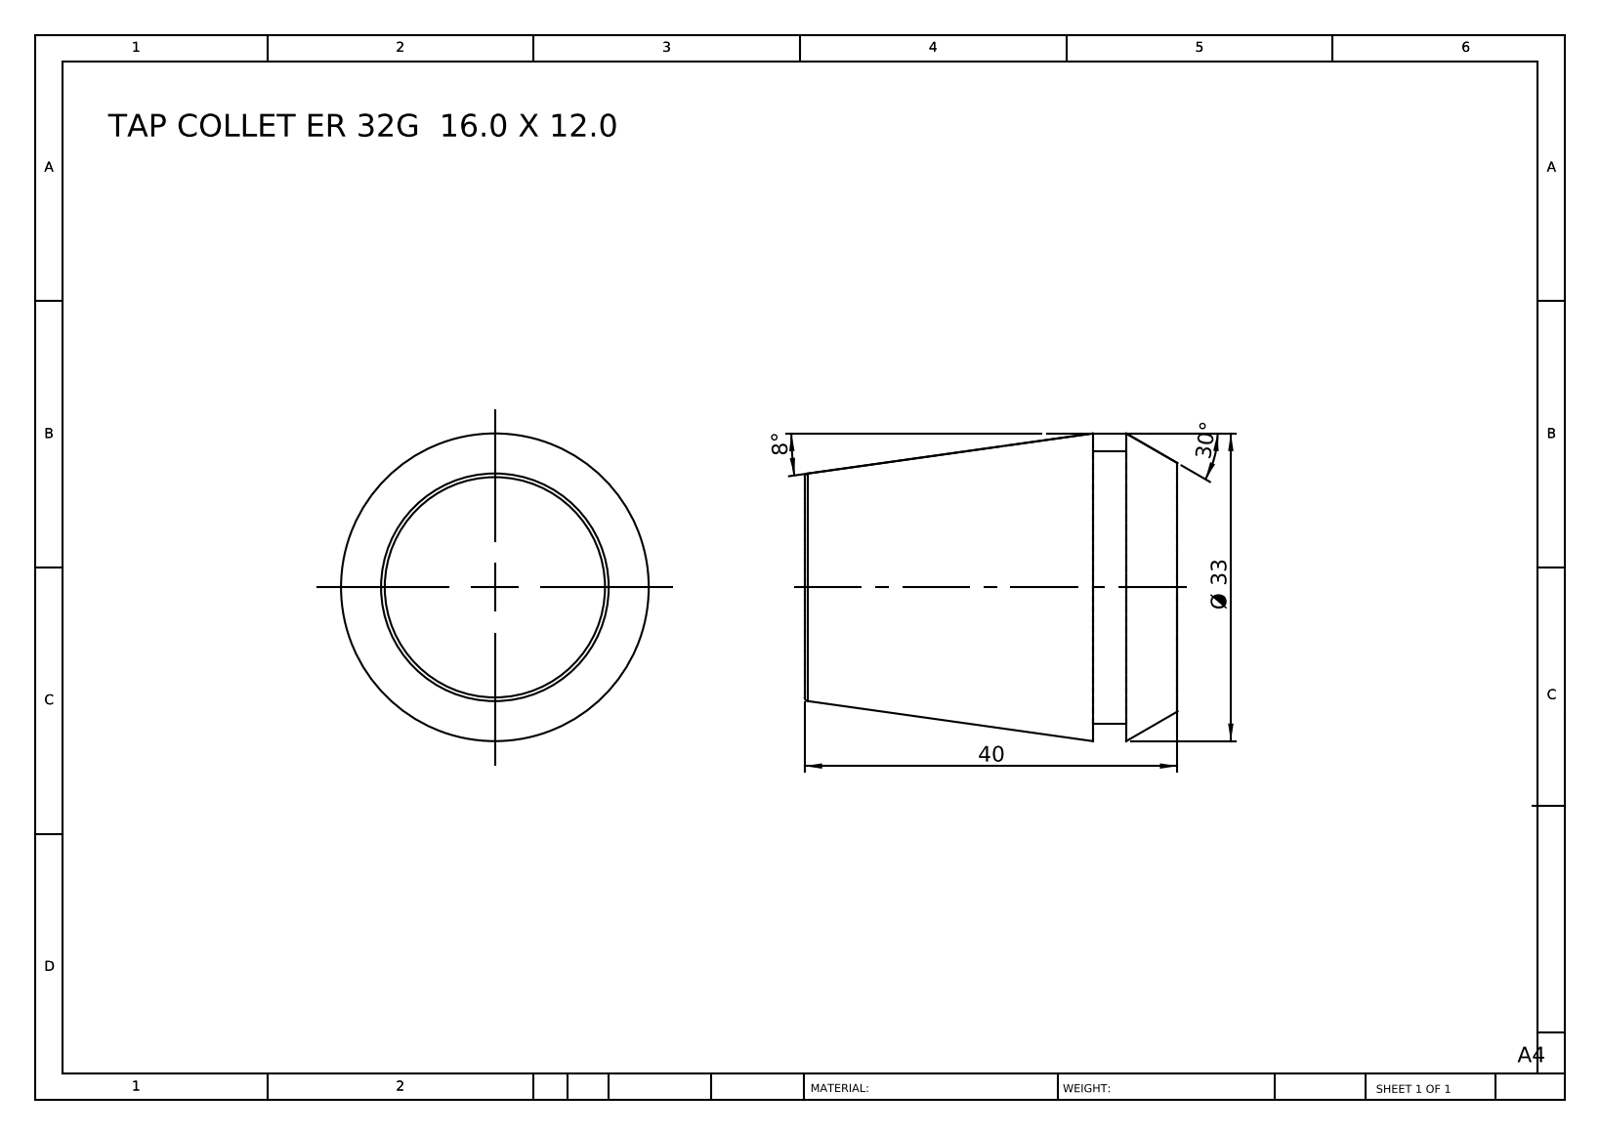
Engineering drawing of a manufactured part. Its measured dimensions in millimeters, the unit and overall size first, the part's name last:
Units: millimetres
Overall size (bounding box): 40 × 33 × 33
Round bosses / shafts (diameter × count): ⌀29.2 ×1
Main face-to-face distances: 40, 9.1, 30.9, 5.5, 3.6, 34.5
Volume: 26 350 mm³ · Surface area: 5 119 mm²
Bodies: 1 solid, 12 faces (4 planar, 2 cylindrical, 6 other)
Part name (STEP PRODUCT): TAP COLLET ER 32G 16.0 X 12.0
STEP written by: SolidWorks 2014 (CONFIG_CONTROL_DESIGN)
